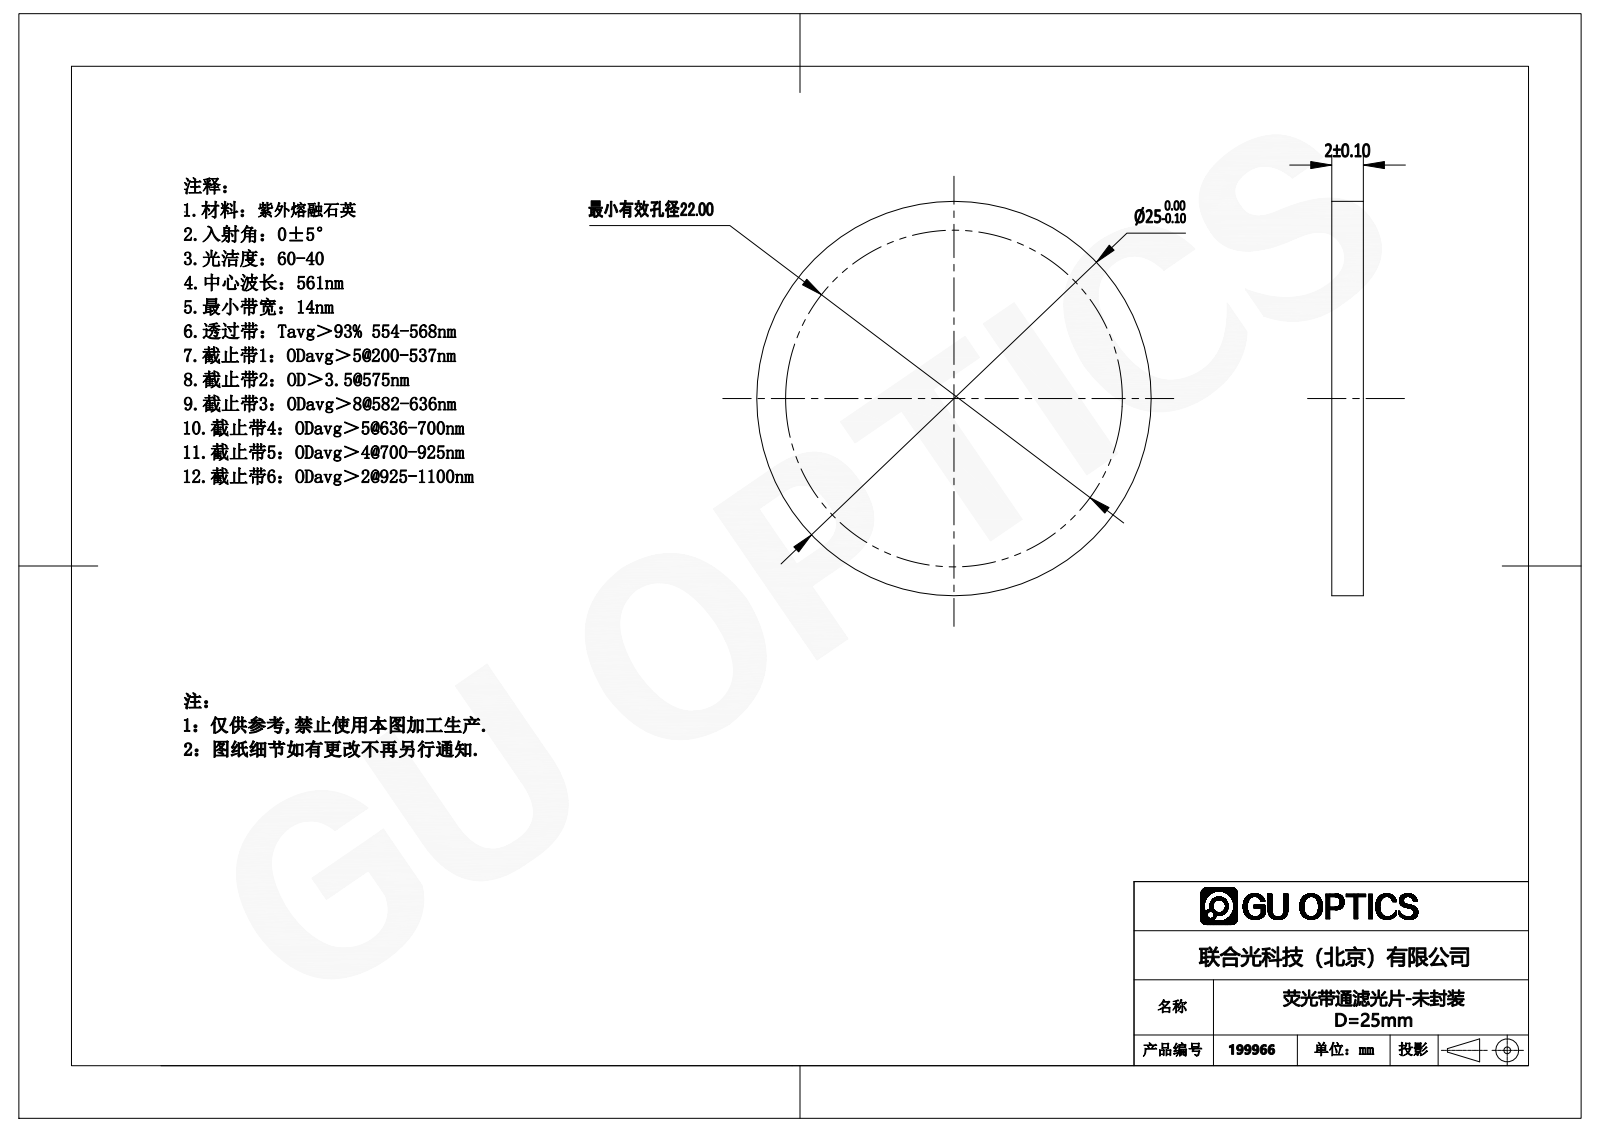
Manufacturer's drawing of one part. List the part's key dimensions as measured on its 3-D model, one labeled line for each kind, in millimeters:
STEP written by: SolidWorks 2016 (AUTOMOTIVE_DESIGN)
Units: millimetres
Bodies: 1 solid, 4 faces (2 planar, 2 cylindrical, 0 other)
Overall size (bounding box): 25 × 25 × 2
Volume: 982 mm³ · Surface area: 1 139 mm²
Round bosses / shafts (diameter × count): ⌀25 ×1
Main face-to-face distances: 2
